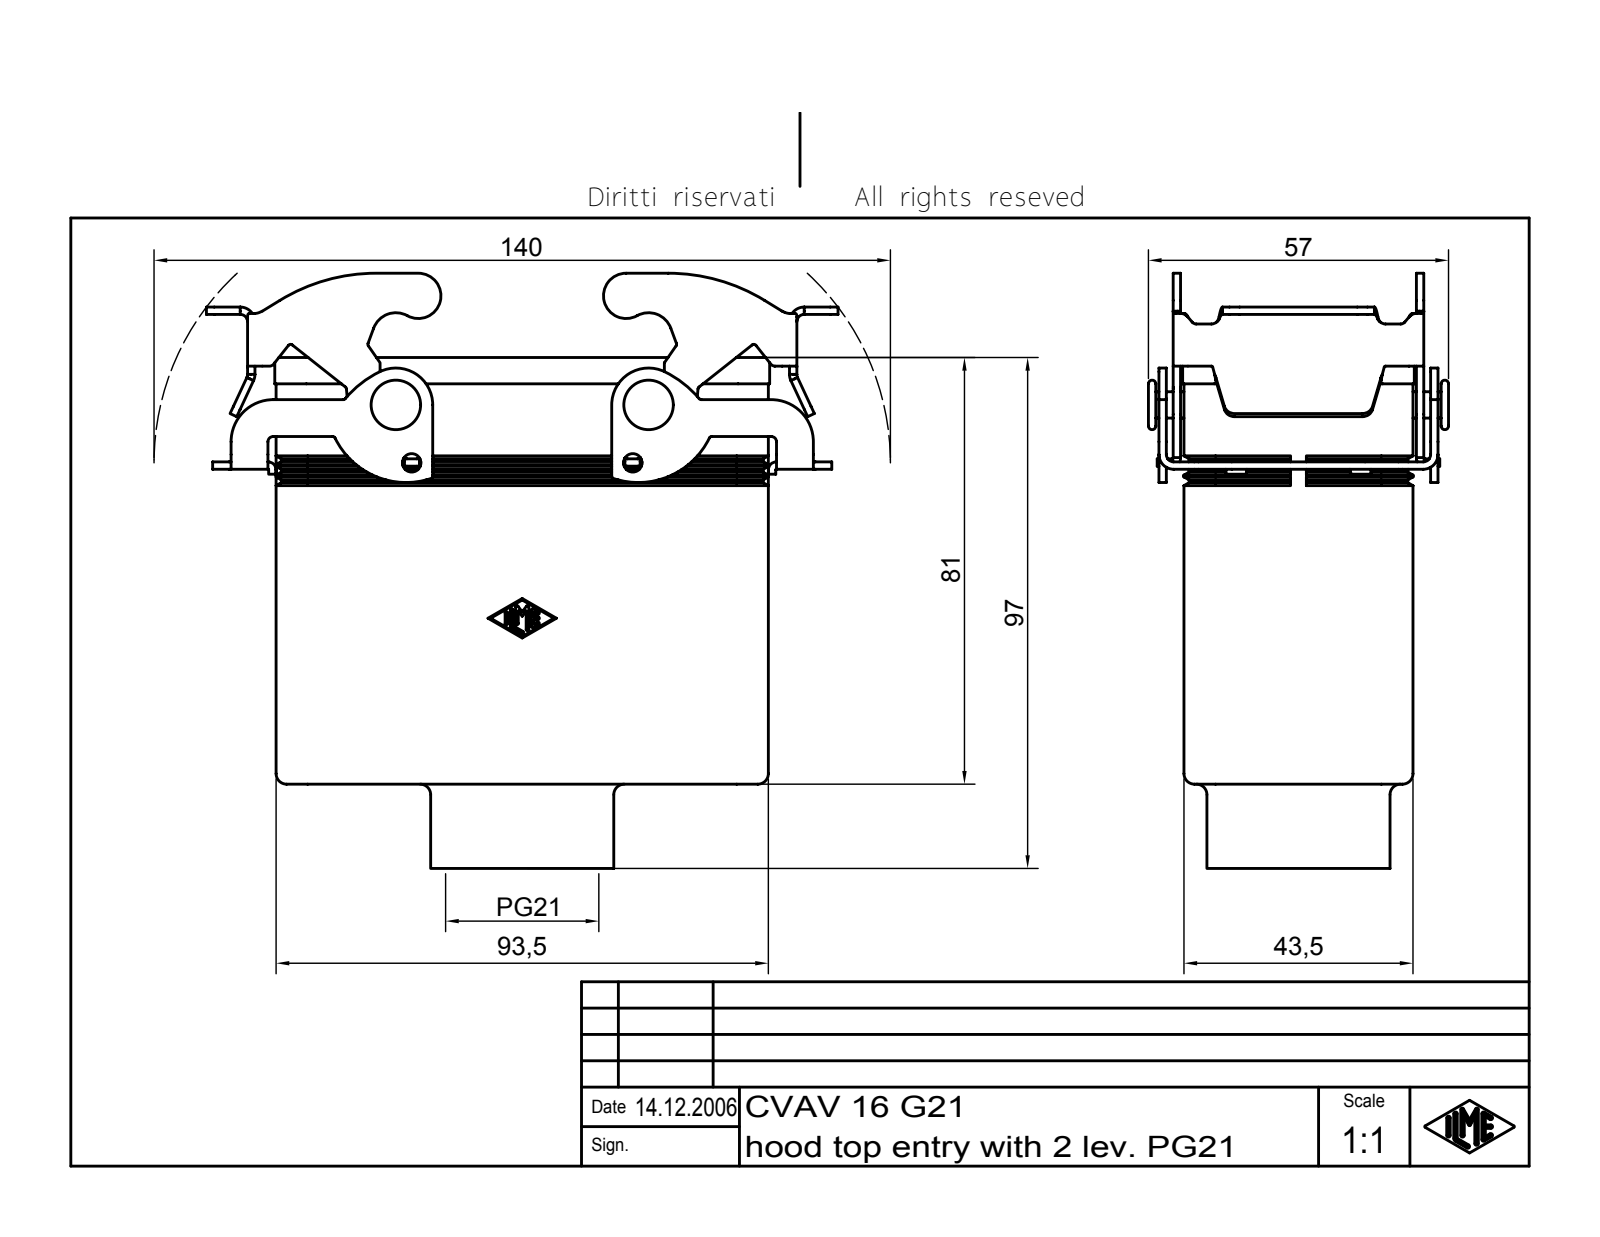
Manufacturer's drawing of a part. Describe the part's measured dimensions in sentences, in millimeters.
The part is named "CVAV 16 G21". Its 3-D file was written by "Autodesk Inventor 7 (AUTOMOTIVE_DESIGN)". It is 3 solids with 714 faces: 207 planar, 186 cylindrical and 321 other. Overall it measures 119.97 by 113 by 57 millimeters. Its volume is 105 921 cubic millimeters and its surface area 69 373 square millimeters. Round holes: 2 of diameter 3.5, 1 of diameter 23.78, 1 of diameter 26.78. Round bosses or shafts: 2 of diameter 5, 2 of diameter 3.2, 1 of diameter 34.78. Partial cylindrical surfaces (rounded edges, fillets, slot ends): 18 of radius 0.5, 16 of radius 0.25, 14 of radius 1, 12 of radius 1.5, 12 of radius 2, 10 of radius 1.4, 10 of radius 2.8, 8 of radius 6. The main face-to-face distances are 3, 40.5, 43.5, 37.5, 1.4, 90.5, 8.5, 93.5, 11.75, 82. The hole center spacings are 42.
